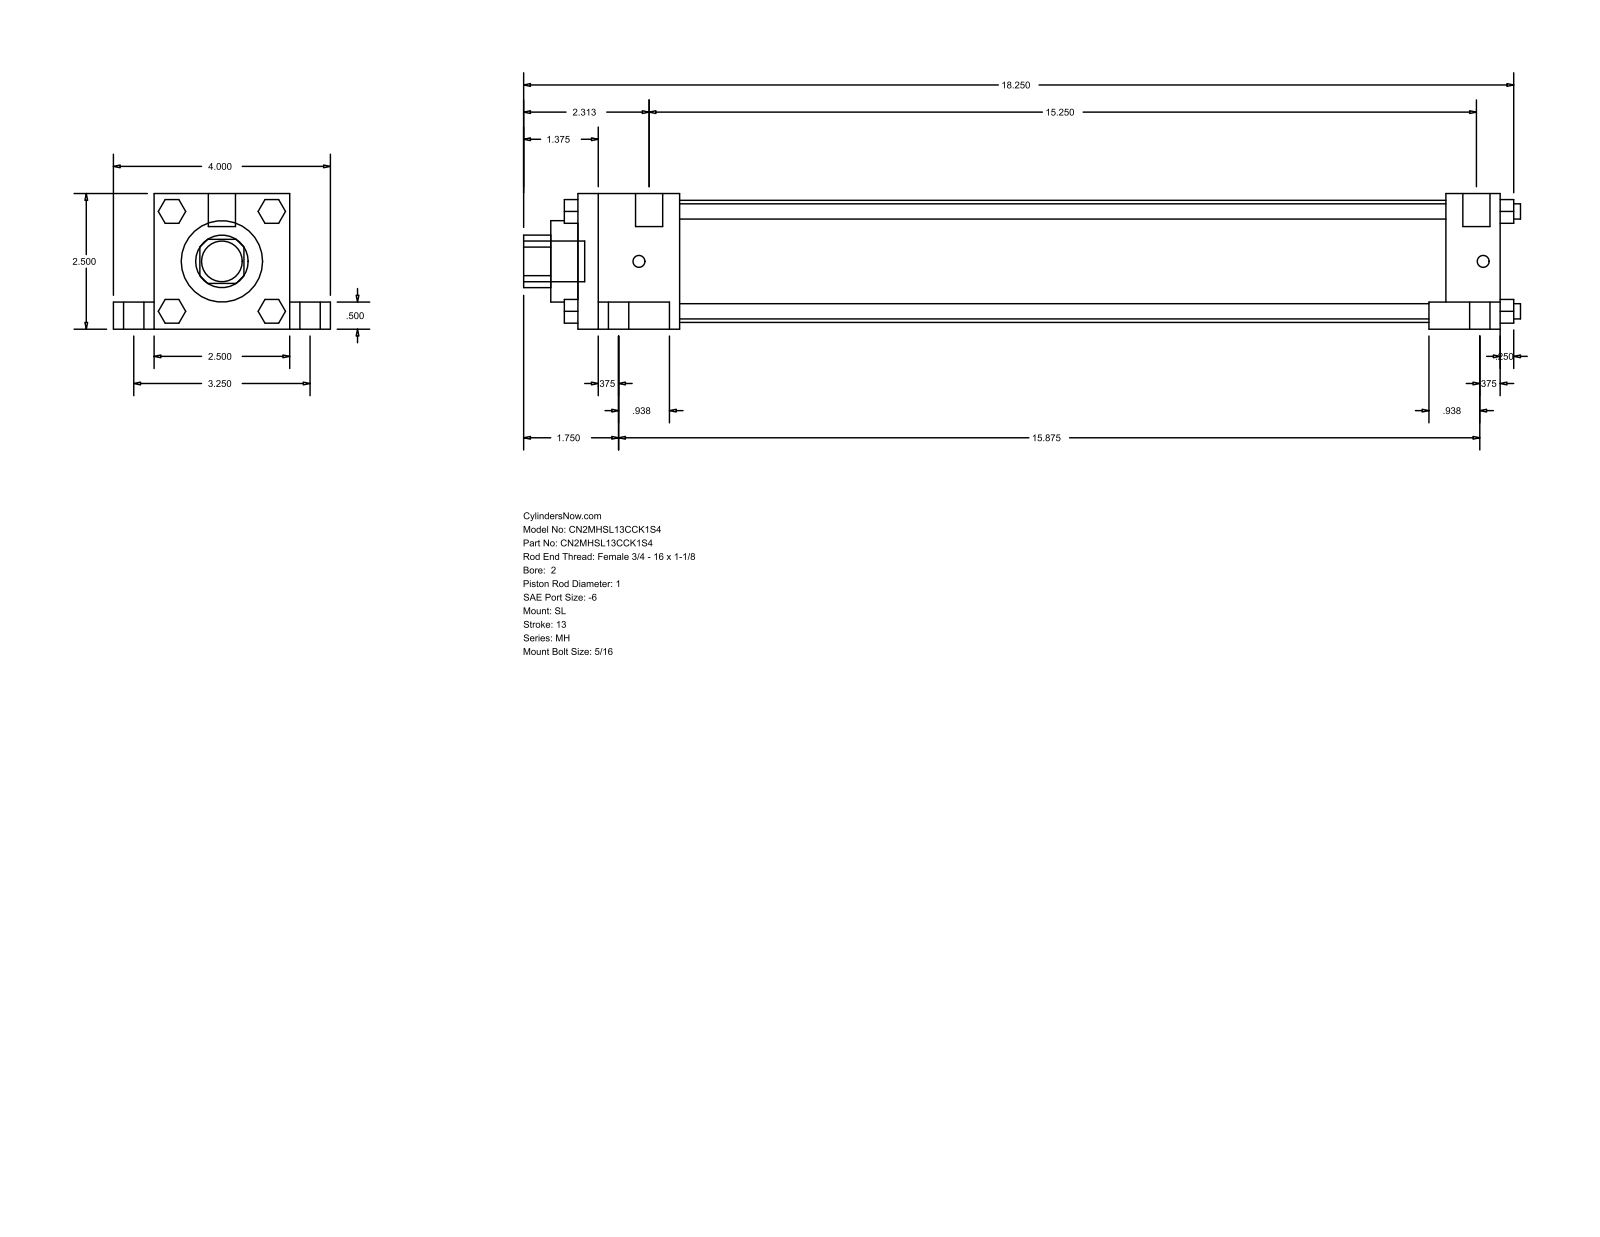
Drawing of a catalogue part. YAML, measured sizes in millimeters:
part_name: "MH_SL__0200_1"
step_written_by: "GSSL Pune (CONFIG_CONTROL_DESIGN)"
units: millimeters
bodies: {solids: 0, faces: 148, planar: 112, cylindrical: 36, other: 0}
overall_size: [466.73, 101.6, 63.5]
round_holes:
  - {diameter: 25.4, count: 1}
  - {diameter: 38.1, count: 1}
  - {diameter: 57.15, count: 1}
round_bosses_or_shafts:
  - {diameter: 15.88, count: 4}
  - {diameter: 9.53, count: 4}
  - {diameter: 7.14, count: 4}
  - {diameter: 5.56, count: 4}
  - {diameter: 12.7, count: 2}
  - {diameter: 19.05, count: 1}
partial_cylinders:
  - {radius: 12.29, count: 1}
face_to_face_distances: [63.5, 431.8, 12.7, 19.05, 50.8, 82.55, 25.4, 9.52, 406.4, 47.63]
